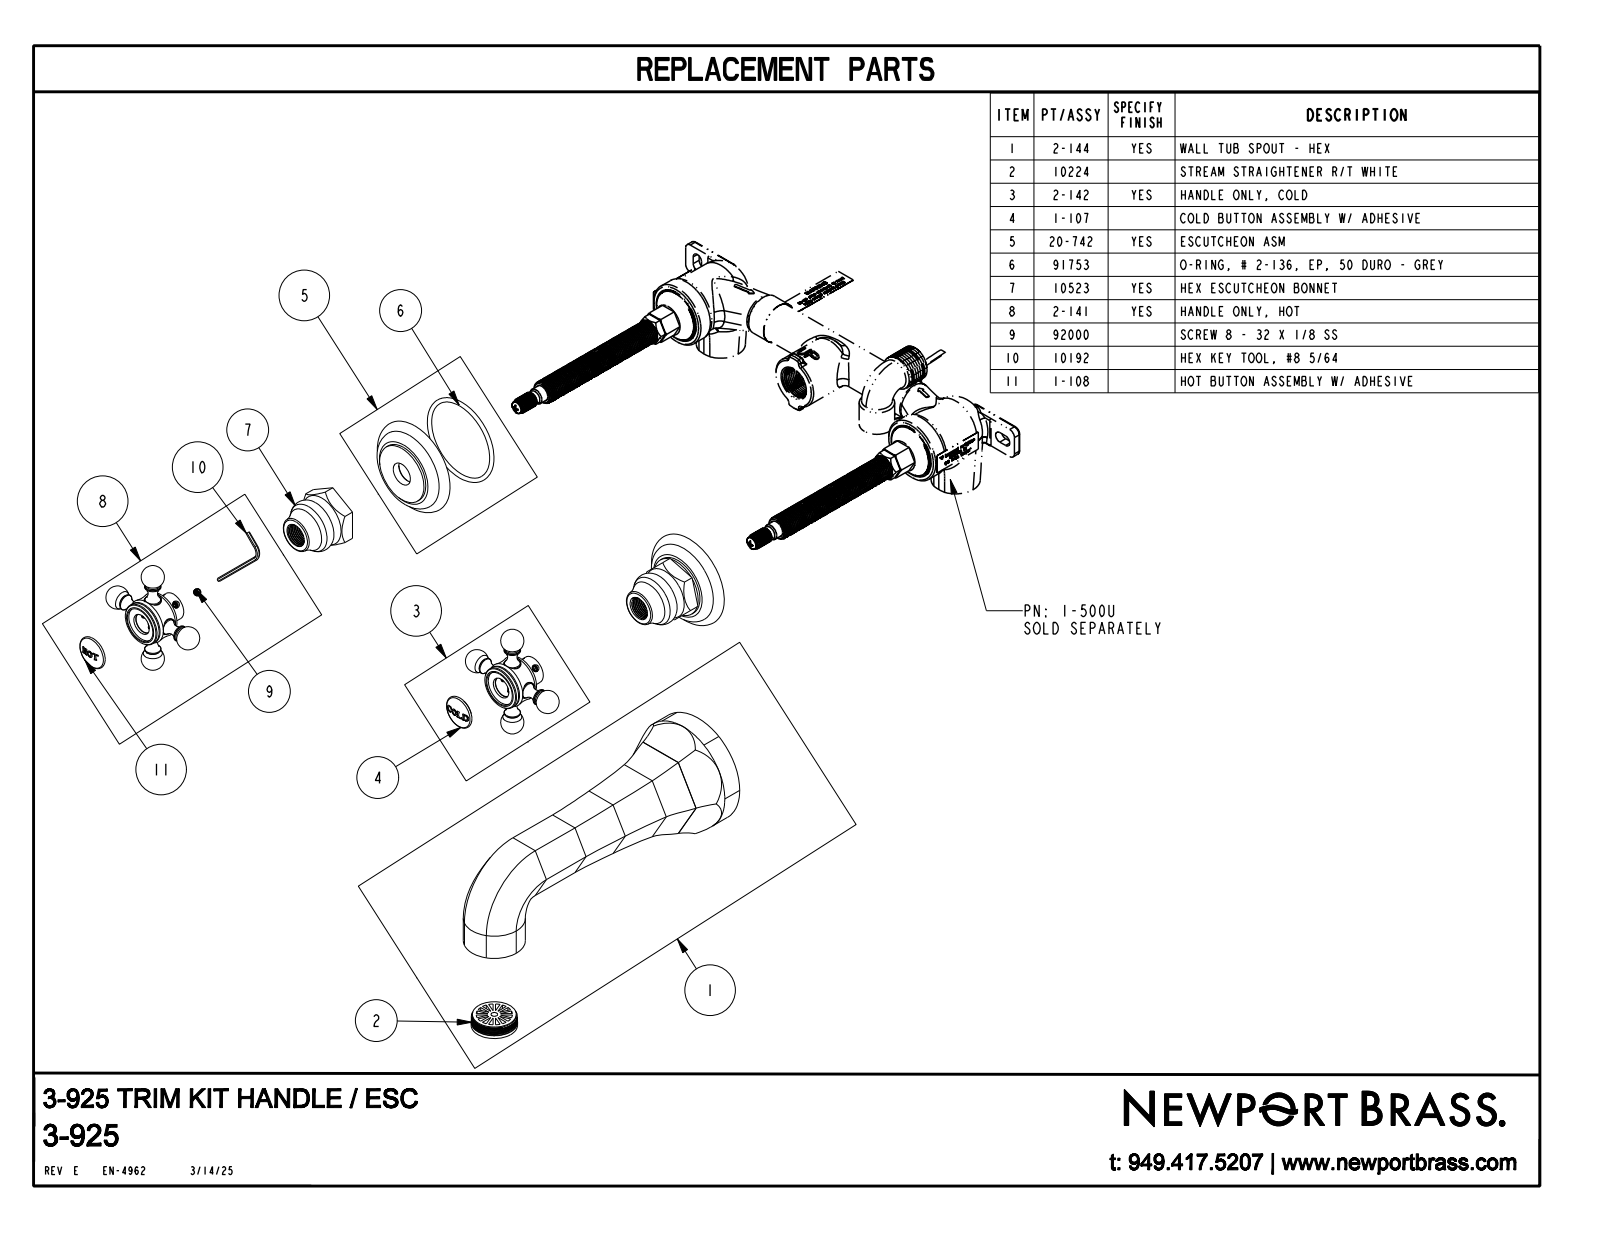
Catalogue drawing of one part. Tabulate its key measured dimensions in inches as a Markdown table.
| quantity | value |
| --- | --- |
| part name | 3-925_SW0002 |
| STEP written by | CREO PARAMETRIC BY PTC INC, 2018400 (AUTOMOTIVE_DESIGN) |
| units | inches |
| bodies | 3 solids, 475 faces (129 planar, 104 cylindrical, 242 other) |
| overall size | 10.789 × 9.103 × 7.562 |
| volume | 27.02 in³ |
| surface area | 101.5 in² |
| round holes (diameter × count) | 0.41 × 4, 0.855 × 2 |
| round bosses / shafts (diameter × count) | 0.392 × 4, 1.482 × 2, 1.055 × 2, 0.687 × 2, 2.8 × 1, 0.266 × 1 |
| partial cylindrical surfaces (radius × count) | 0.006 × 7, 0.024 × 7, 2.125 × 6, 0.03 × 5, 0.048 × 3, 0.018 × 2, 0.036 × 2, 0.041 × 2 |
| main face-to-face distances | 1.299, 0.995, 2.294, 1.313, 0.375, 1.313, 0.437, 0.062, 1.687, 1.312 |
| hole center spacings | 7.874 |
